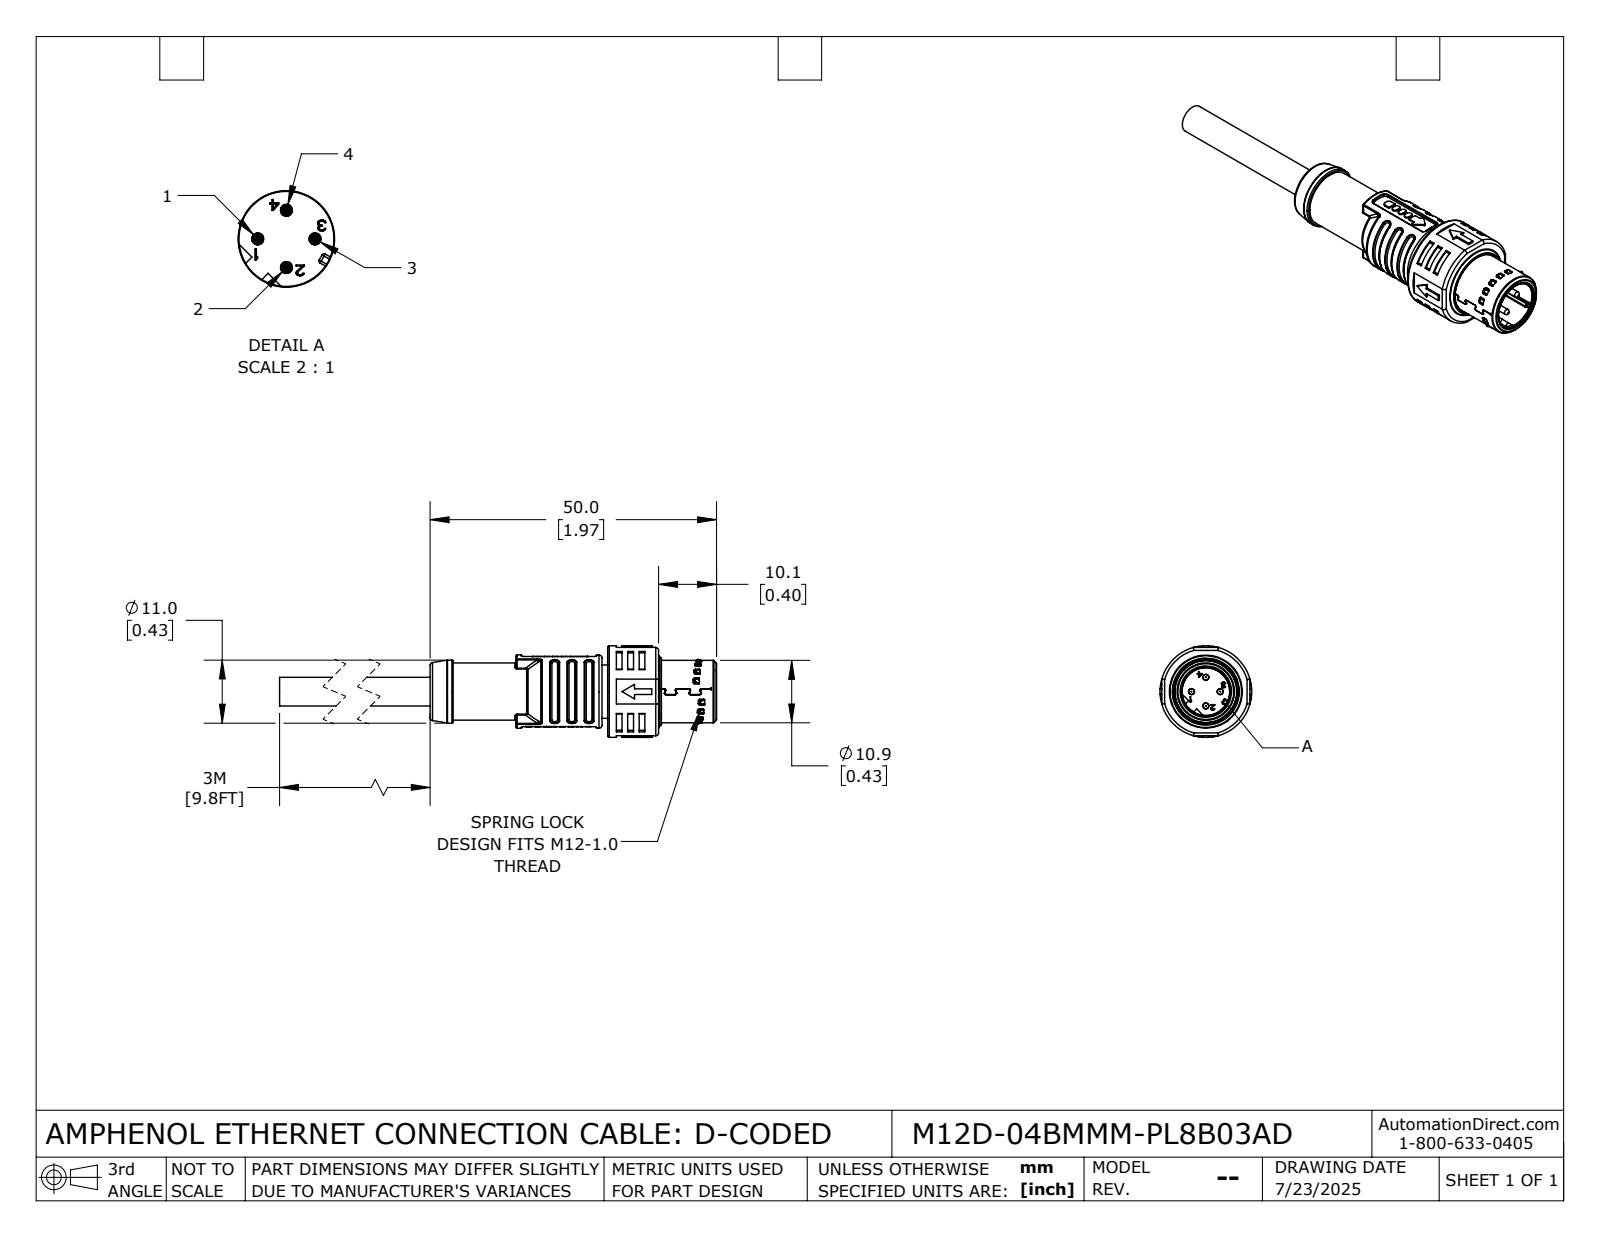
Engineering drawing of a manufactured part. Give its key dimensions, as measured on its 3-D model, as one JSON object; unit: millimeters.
{"part_name": "M12D-04BMMM-PL8B03AD", "step_written_by": "SolidWorks 2024 (CONFIG_CONTROL_DESIGN)", "units": "millimeters", "bodies": {"solids": 1, "faces": 2139, "planar": 996, "cylindrical": 644, "other": 499}, "overall_size": [80, 16, 16], "volume_mm3": 5399, "surface_area_mm2": 5961, "round_holes": [[1.05, 4], [8.3, 1], [9, 1], [10.15, 1], [10.5, 1], [10.9, 1], [11.5, 1], [11.8, 1], [14.2, 1]], "round_bosses_or_shafts": [[1, 4], [16, 1], [14.1, 1], [12.8, 1], [12.4, 1], [11, 1], [10.45, 1], [10.4, 1]], "partial_cylinders_radius": [[0.2, 119], [0.25, 66], [0.3, 64], [0.15, 44], [0.5, 38], [0.13, 12], [0.7, 11], [0.1, 7]], "face_to_face_distances": [1, 30, 10.1, 8.9, 2.5, 1.2, 8.6, 32.5, 15.4, 1.5], "hole_center_spacings": [2.5, 3.54, 5]}
